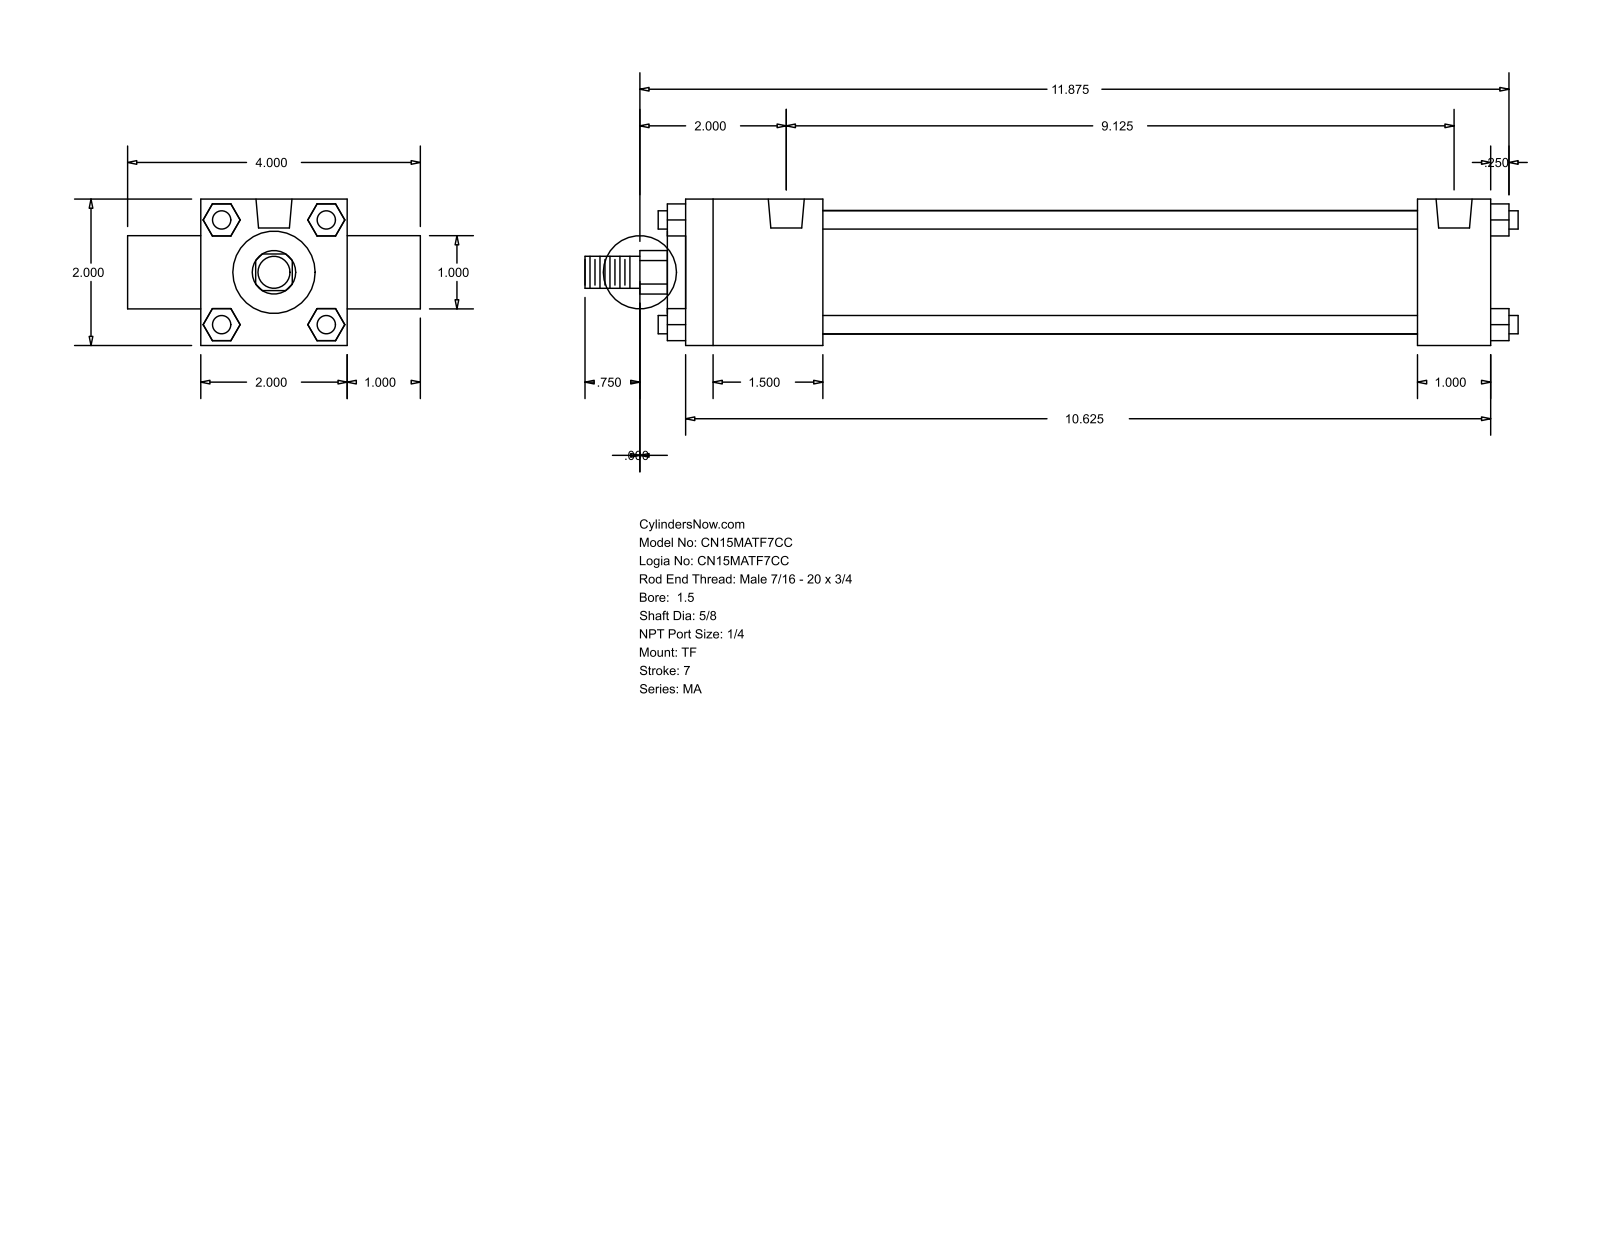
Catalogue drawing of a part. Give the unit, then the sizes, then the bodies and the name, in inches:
Units: inches
Overall size (bounding box): 12.75 × 4 × 2
Round holes (diameter × count): ⌀0.313 ×3, ⌀0.492 ×2
Round bosses / shafts (diameter × count): ⌀0.25 ×4, ⌀1.69 ×1, ⌀1.125 ×1, ⌀1 ×1, ⌀0.625 ×1, ⌀0.437 ×1
Partial cylindrical surfaces — rounded edges, fillets, slot ends (radius × count): R0.297 ×1
Main face-to-face distances: 2, 11, 1, 0.25, 11.25, 3, 1.875, 10, 8.125, 9.125
Hole centre spacings: 9.125
Bodies: 0 solids, 120 faces (92 planar, 28 cylindrical, 0 other)
Part name (STEP PRODUCT): MA_TF__0150_0.625
STEP written by: GSSL Pune (CONFIG_CONTROL_DESIGN)
